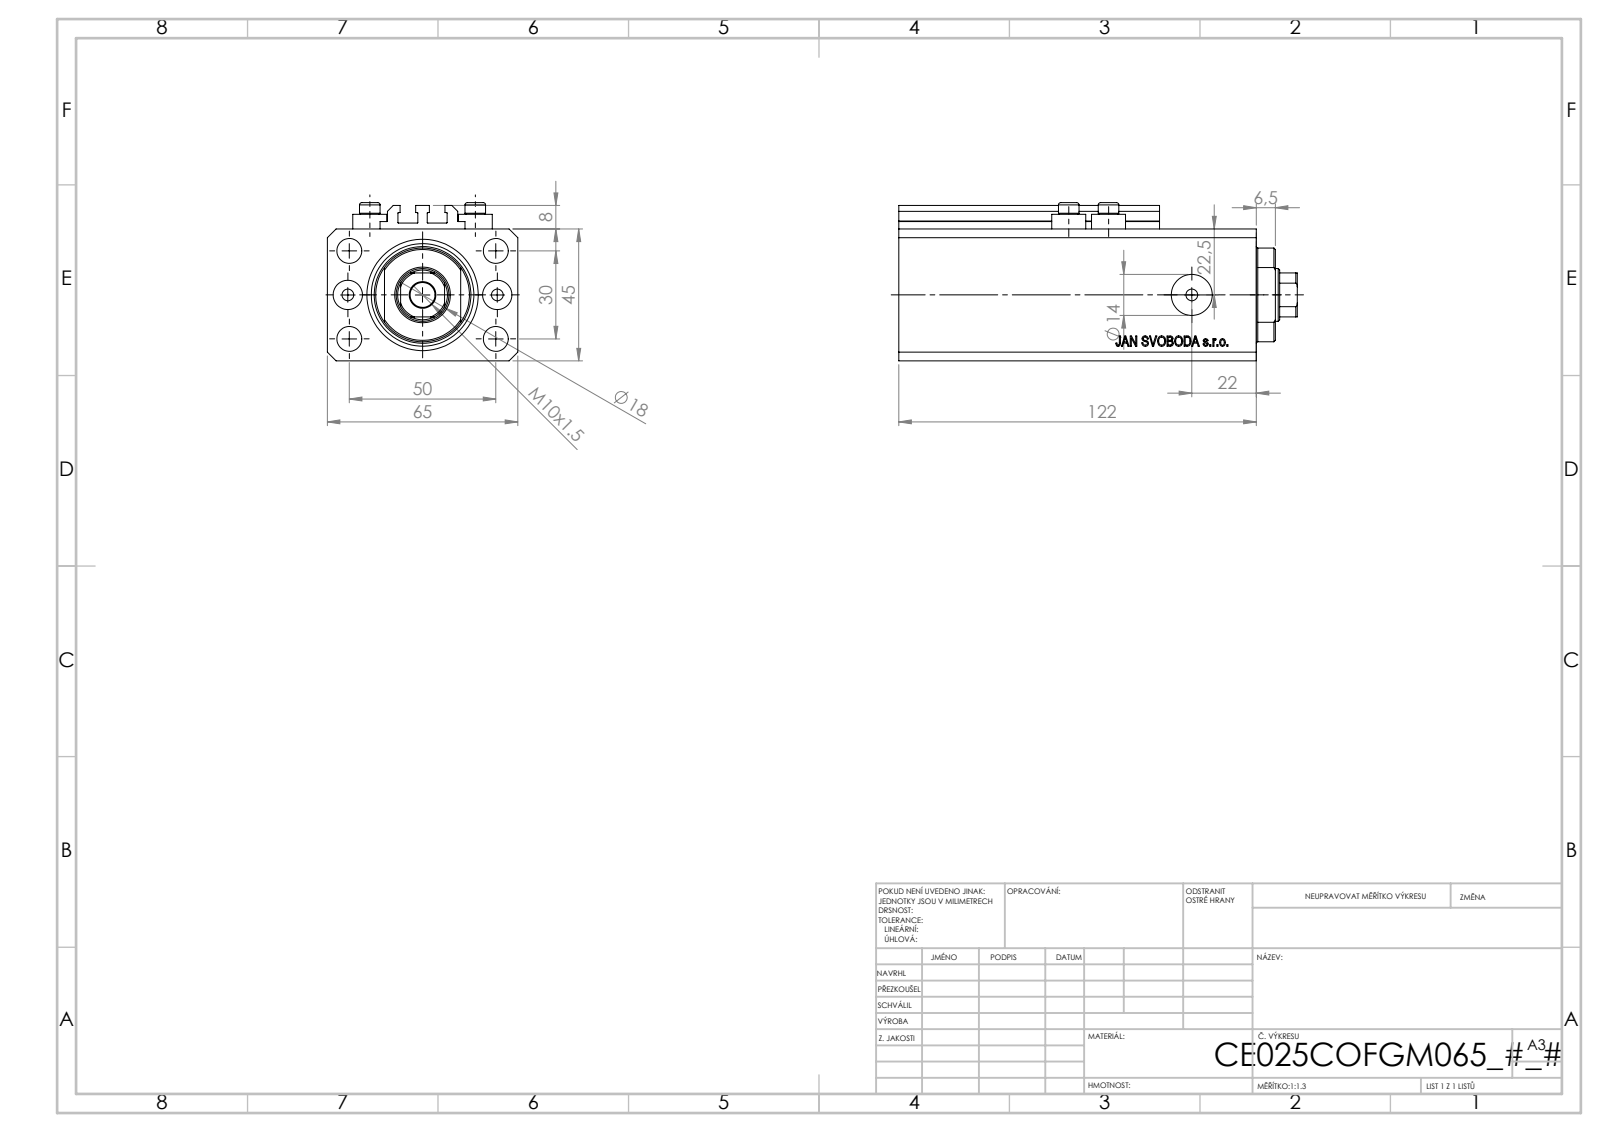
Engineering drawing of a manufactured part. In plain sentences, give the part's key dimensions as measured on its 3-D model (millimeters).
The part is named "V250CE_C_VCP; V250CE_VC_C; ALLEN BOLT V250CE; V250CE_C_Body". Its 3-D file was written by "SolidWorks 2019 (CONFIG_CONTROL_DESIGN)". It is 8 solids with 1034 faces: 504 planar, 86 cylindrical and 444 other. Overall it measures 136 by 65 by 54 millimeters. Its volume is 327 580 cubic millimeters and its surface area 82 271 square millimeters. Round holes: 8 of diameter 4, 5 of diameter 8.5, 2 of diameter 10, 2 of diameter 14, 1 of diameter 18, 1 of diameter 25, 1 of diameter 38. Round bosses or shafts: 4 of diameter 11.6, 4 of diameter 7. Partial cylindrical surfaces (rounded edges, fillets, slot ends): 10 of radius 0.2, 1 of radius 8.5, 1 of radius 16. The main face-to-face distances are 45, 65, 14, 47, 108, 122, 2.5, 10, 2, 20.5. The hole center spacings are 15.01, 29.15, 52.68, 13.6, 25.5, 30, 36, 38.48.
